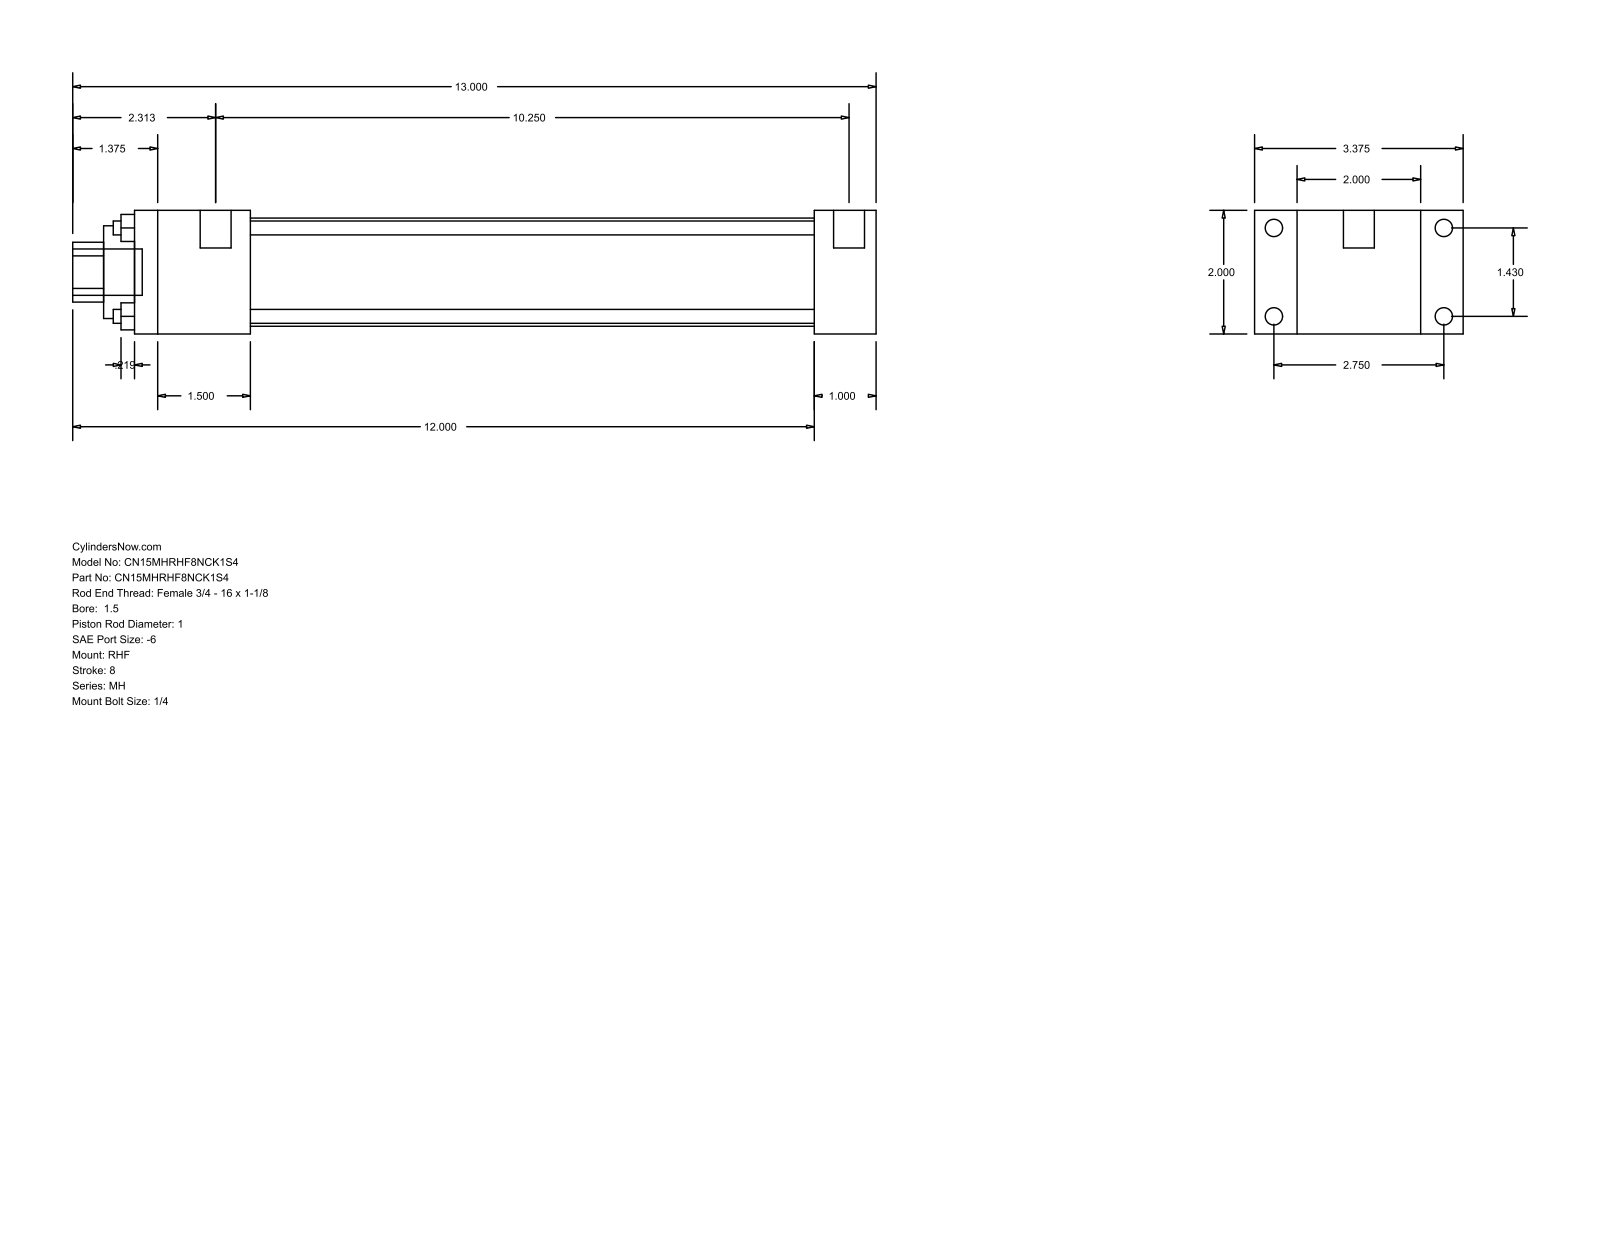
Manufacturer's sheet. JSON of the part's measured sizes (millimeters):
{"part_name": "MH_RHF__0150_1", "step_written_by": "GSSL Pune (CONFIG_CONTROL_DESIGN)", "units": "millimeters", "bodies": {"solids": 0, "faces": 88, "planar": 60, "cylindrical": 28, "other": 0}, "overall_size": [330.2, 85.72, 50.8], "round_holes": [[5.71, 4], [25.4, 1], [38.1, 1], [44.45, 1]], "round_bosses_or_shafts": [[7.14, 4], [5.56, 4], [12.7, 2], [19.05, 1]], "partial_cylinders_radius": [[12.29, 1]], "face_to_face_distances": [50.8, 25.4, 17.46, 68.26, 85.72, 304.8, 279.4, 47.63, 231.77, 257.17], "hole_center_spacings": [25.68, 36.32, 51.36]}
